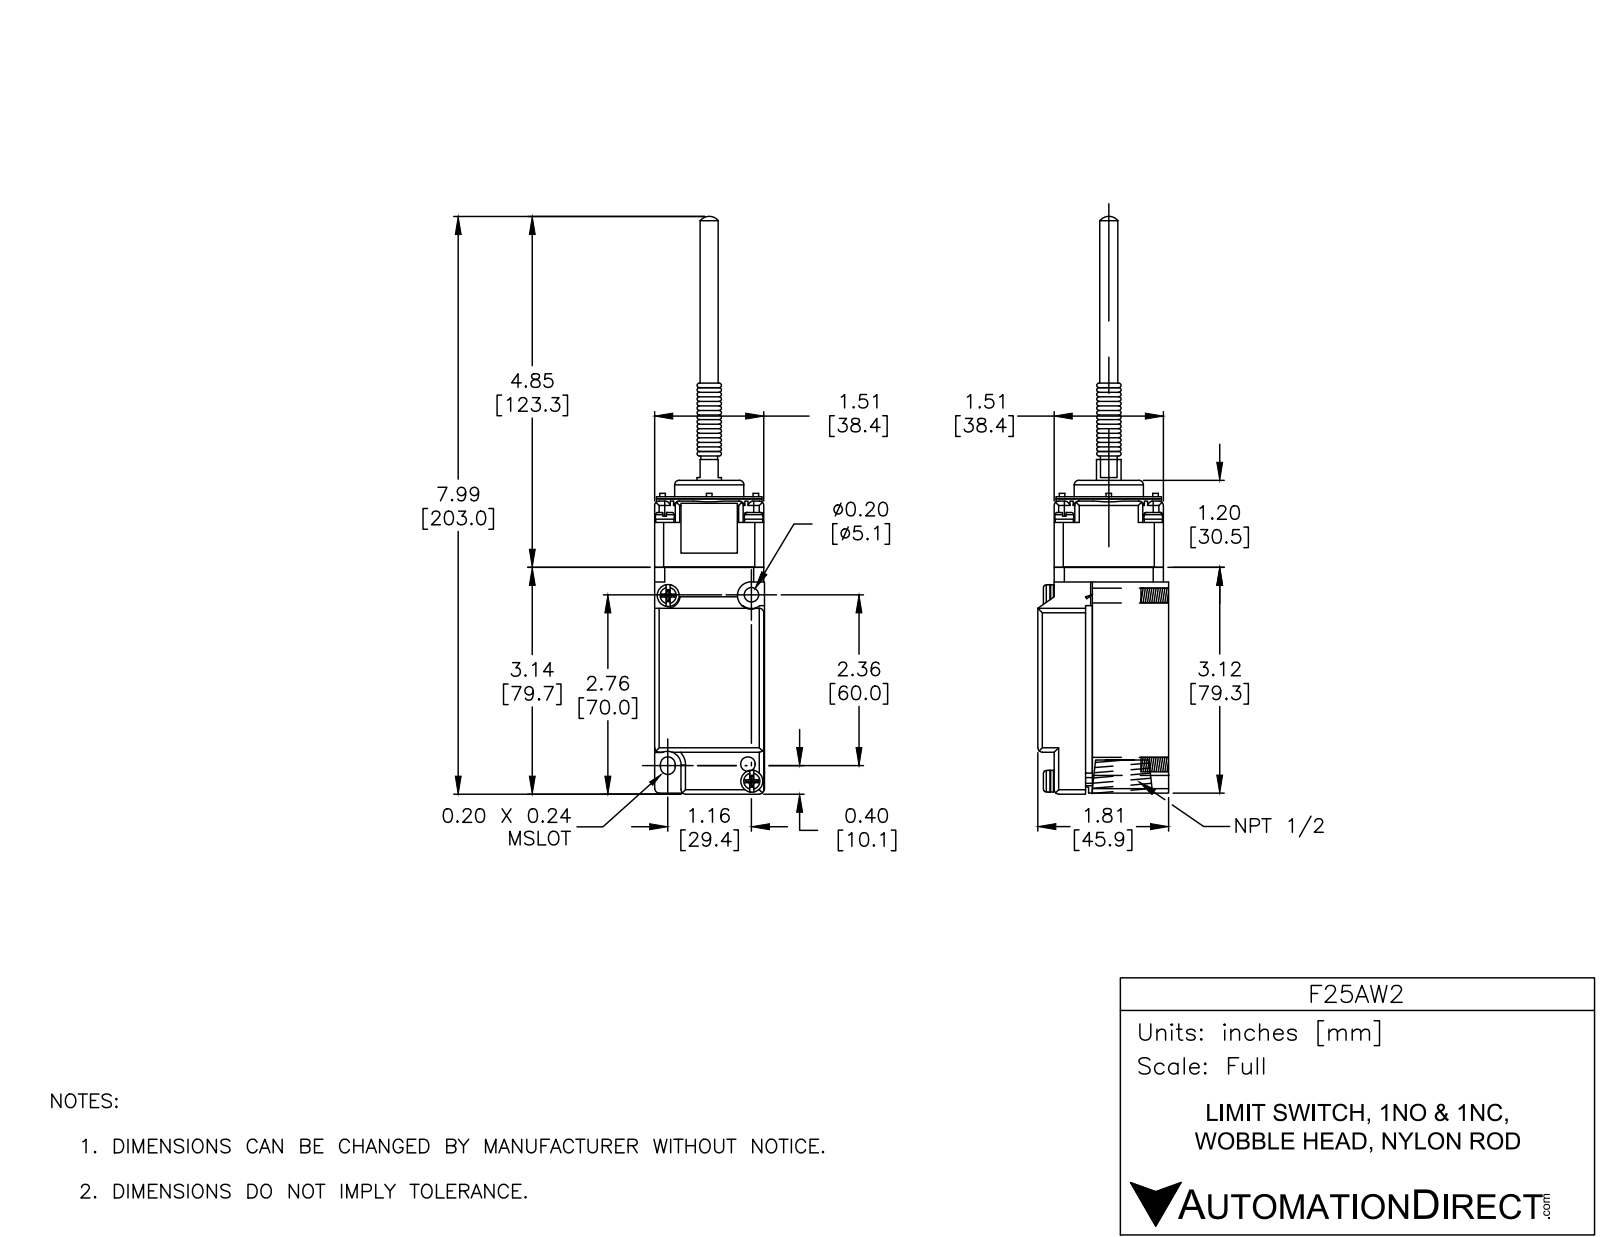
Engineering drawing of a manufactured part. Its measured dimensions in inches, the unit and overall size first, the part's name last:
Units: inches
Overall size (bounding box): 7.992 × 1.809 × 1.52
Round holes (diameter × count): ⌀0.077 ×4, ⌀0.177 ×4, ⌀0.19 ×3, ⌀0.2 ×3, ⌀0.23 ×1, ⌀0.92 ×1, ⌀1.054 ×1
Round bosses / shafts (diameter × count): ⌀0.25 ×5, ⌀0.26 ×4, ⌀0.14 ×4, ⌀0.302 ×2, ⌀0.3 ×2, ⌀1.458 ×1, ⌀0.956 ×1, ⌀0.4 ×1
Partial cylindrical surfaces — rounded edges, fillets, slot ends (radius × count): R0.062 ×21, R0.03 ×16, R0.015 ×8, R0.062 ×8, R0.14 ×4, R0.145 ×4, R0.102 ×2, R0.188 ×2
Main face-to-face distances: 0.094, 1.149, 1.055, 1.52, 0.945, 0.66, 0.754, 1.809, 1.51, 0.433
Hole centre spacings: 1.403, 0.616, 0.646, 0.616, 0.87, 0.87, 0.913, 0.914
Volume: 10.1 in³ · Surface area: 78.21 in²
Bodies: 31 solids, 731 faces (247 planar, 136 cylindrical, 348 other)
Part name (STEP PRODUCT): F25AW2
STEP written by: SolidWorks 2018 (AUTOMOTIVE_DESIGN)
